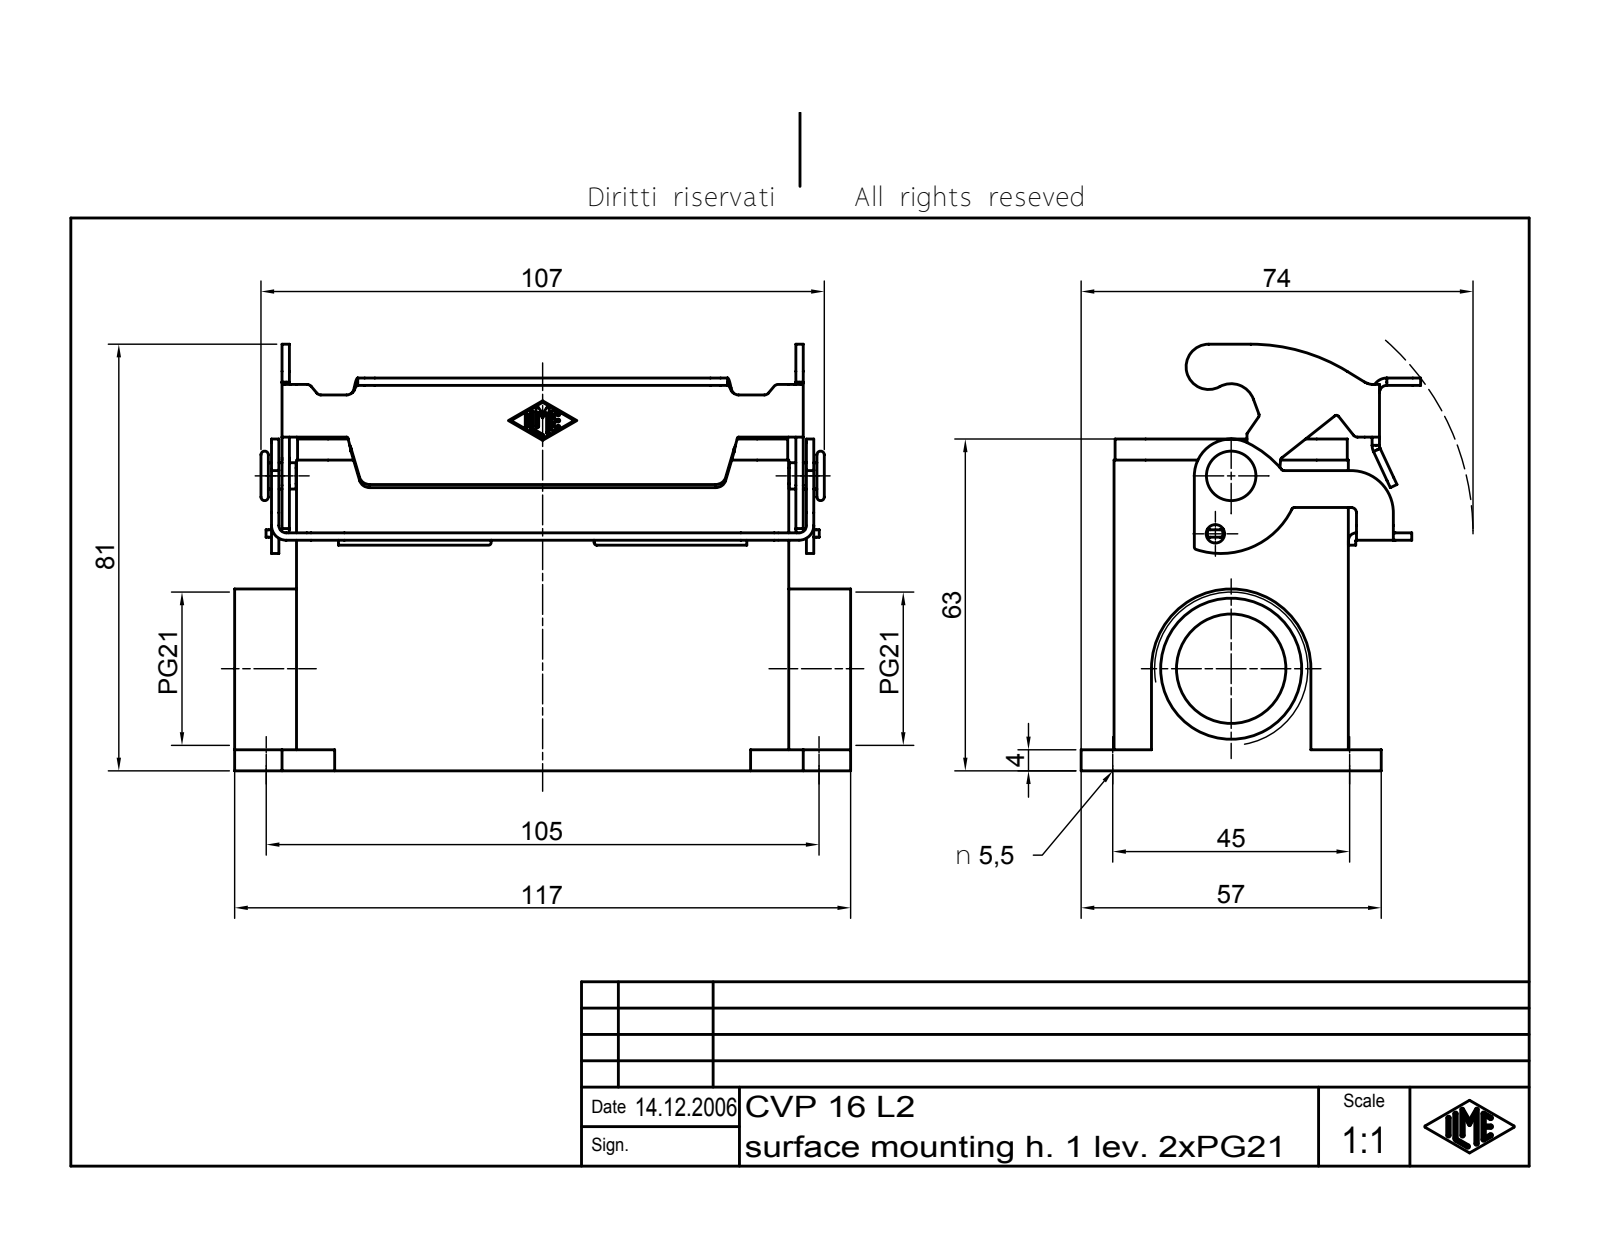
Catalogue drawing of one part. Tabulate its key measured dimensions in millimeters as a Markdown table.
| quantity | value |
| --- | --- |
| part name | CVP 16 L2 |
| STEP written by | Autodesk Inventor 7 (AUTOMOTIVE_DESIGN) |
| units | millimeters |
| bodies | 2 solids, 401 faces (141 planar, 116 cylindrical, 144 other) |
| overall size | 117 × 81 × 64.48 |
| volume | 107 514 mm³ |
| surface area | 58 048 mm² |
| round holes (diameter × count) | 5.5 × 4, 3.5 × 1, 20.78 × 1, 26.78 × 1 |
| round bosses / shafts (diameter × count) | 5 × 1, 3.2 × 1, 3 × 1 |
| partial cylindrical surfaces (radius × count) | 0.25 × 15, 0.5 × 9, 1.5 × 9, 1 × 8, 1.4 × 6, 2 × 6, 2.8 × 6, 1.8 × 4 |
| main face-to-face distances | 4, 40.5, 44.5, 36.5, 1.4, 11.5, 82, 40.3, 4.2, 89.5 |
| hole center spacings | 45, 105, 114.24, 25.79 |
